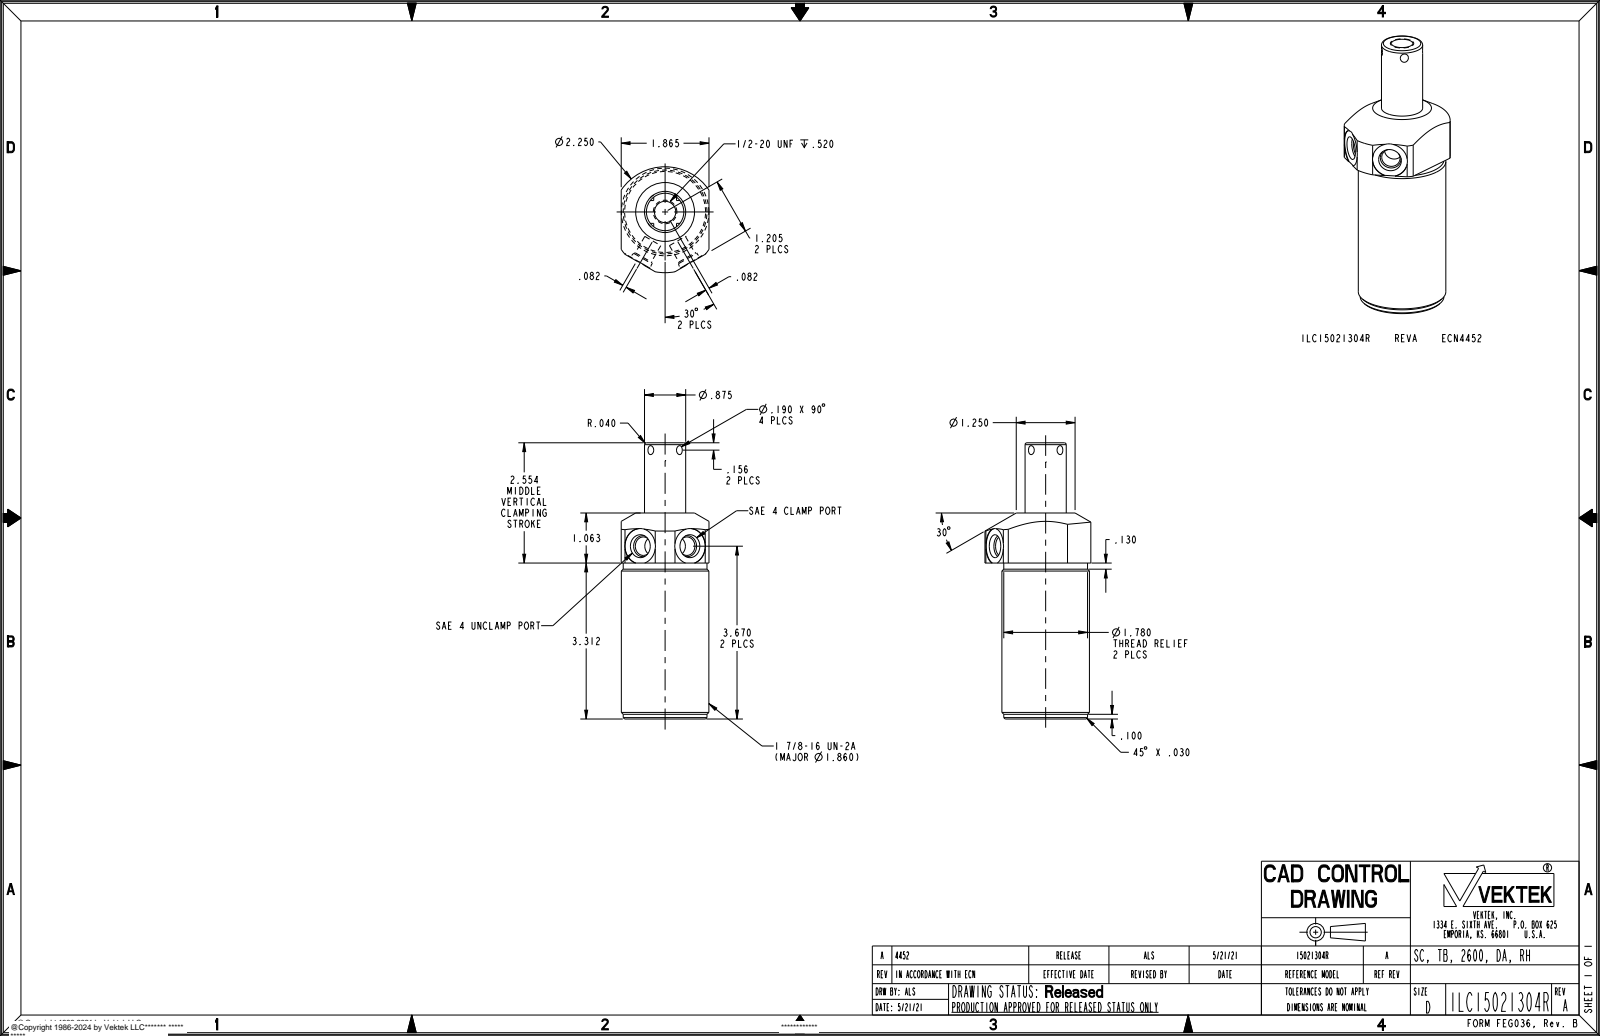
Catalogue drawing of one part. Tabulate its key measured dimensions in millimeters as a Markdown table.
| quantity | value |
| --- | --- |
| part name | ILC15021304R |
| STEP written by | PRO/ENGINEER BY PARAMETRIC TECHNOLOGY CORPORATION, 2013320 (CONFIG_CONTROL_DESIGN) |
| units | millimeters |
| bodies | 1 solid, 71 faces (19 planar, 24 cylindrical, 28 other) |
| overall size | 149 × 57.2 × 47.4 |
| volume | 213 400 mm³ |
| surface area | 25 590 mm² |
| round holes (diameter × count) | 10 × 2, 19.1 × 2, 11.5 × 1 |
| round bosses / shafts (diameter × count) | 47.2 × 1, 45.2 × 1, 22.2 × 1, 12.7 × 1 |
| partial cylindrical surfaces (radius × count) | 28.6 × 1 |
| main face-to-face distances | 84.1, 47.4, 111.1, 27, 149, 64.9, 37.9, 13.5, 13.7, 135.8 |
